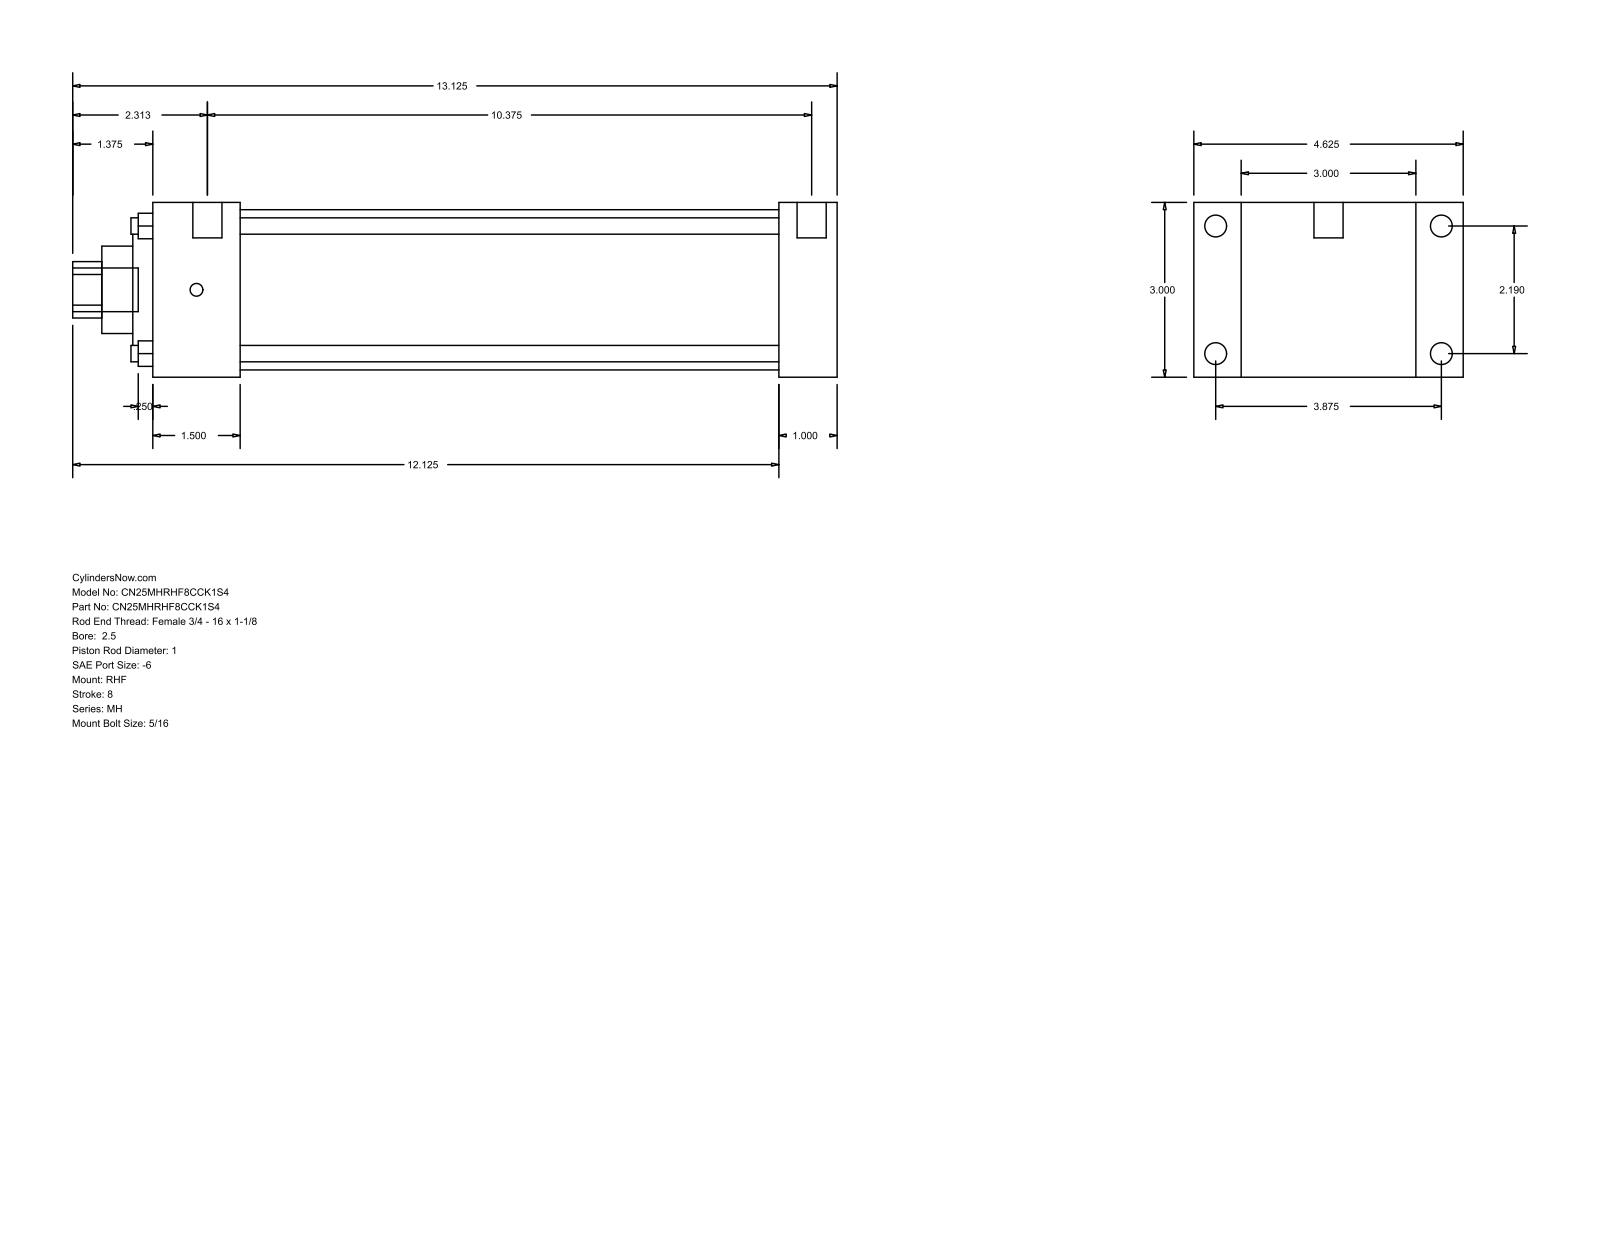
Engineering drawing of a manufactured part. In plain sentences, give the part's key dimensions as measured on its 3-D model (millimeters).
The part is named "MH_RHF__0250_1". Its 3-D file was written by "GSSL Pune (CONFIG_CONTROL_DESIGN)". It is 0 solids with 90 faces: 61 planar, 29 cylindrical and 0 other. Overall it measures 333.38 by 117.47 by 76.2 millimeters. Round holes: 4 of diameter 7.14, 1 of diameter 25.4, 1 of diameter 38.1, 1 of diameter 60.33, 1 of diameter 69.85. Round bosses or shafts: 4 of diameter 9.53, 4 of diameter 5.56, 2 of diameter 12.7, 1 of diameter 19.05. Partial cylindrical surfaces (rounded edges, fillets, slot ends): 1 of radius 12.29. The main face-to-face distances are 76.2, 25.4, 20.64, 96.84, 273.06, 298.46, 117.48, 38.11, 234.95, 260.35. The hole center spacings are 39.33, 55.62, 78.66.
